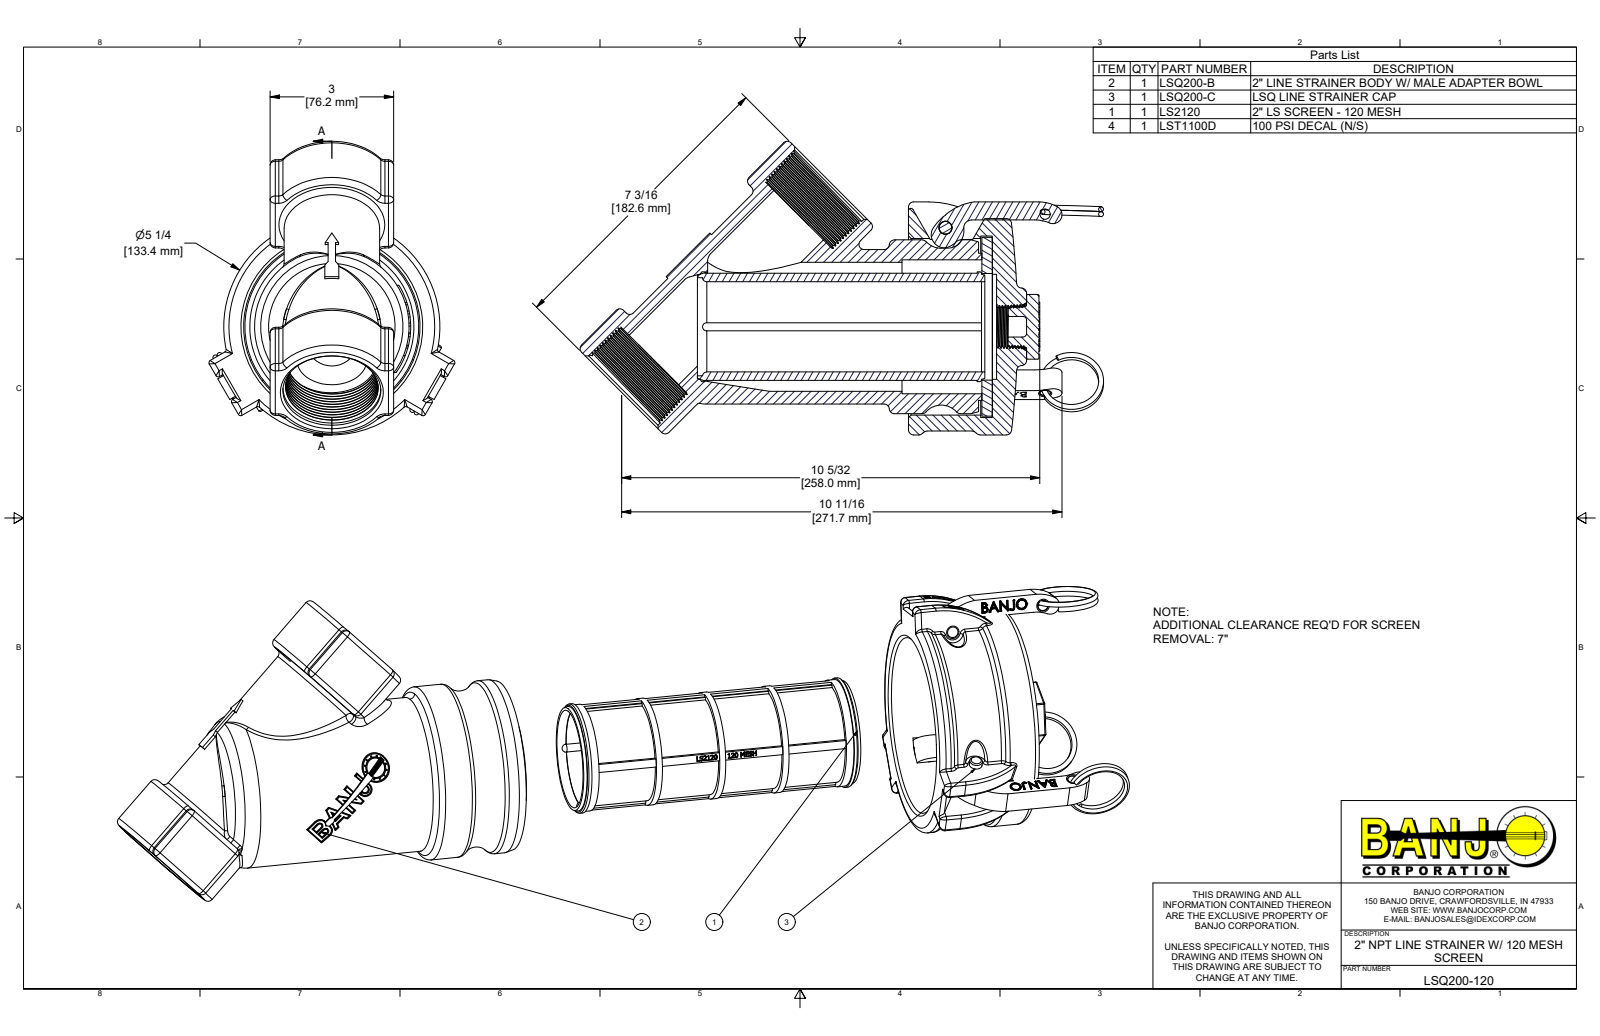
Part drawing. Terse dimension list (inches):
name: LSQ200-120; LSQ200-B; LSQ200-C; LSQ200-MYC (+8 more)
written by: Autodesk Inventor 2019 (AUTOMOTIVE_DESIGN)
unit: in
bodies: 15 solids, 3466 faces (1210 planar, 828 cylindrical, 1428 other)
size: 19.064 × 7.127 × 5.974
volume: 75.45 in³; area: 636.1 in²
holes: 3× ⌀0.25, 3× ⌀0.312, 3× ⌀0.319, 2× ⌀1.7, 1× ⌀0.454, 1× ⌀0.5, 1× ⌀0.641, 1× ⌀2.19, 1× ⌀2.35, 1× ⌀2.55, 1× ⌀2.59, 1× ⌀3.13
bosses: 3× ⌀0.325, 3× ⌀0.311, 1× ⌀5.25, 1× ⌀4.34, 1× ⌀4.22, 1× ⌀3.75, 1× ⌀3.57, 1× ⌀2.666
rounds: 353× R0.006, 51× R0.005, 47× R0.125, 27× R0.06, 18× R0.03, 6× R0.929, 5× R0.25, 4× R0.1
face distances: 0.25, 0.255, 2.04, 2.035, 1.785, 0.45, 0.61, 0.1, 0.355, 0.03
hole spacings: 2.442, 3.359, 5.685
